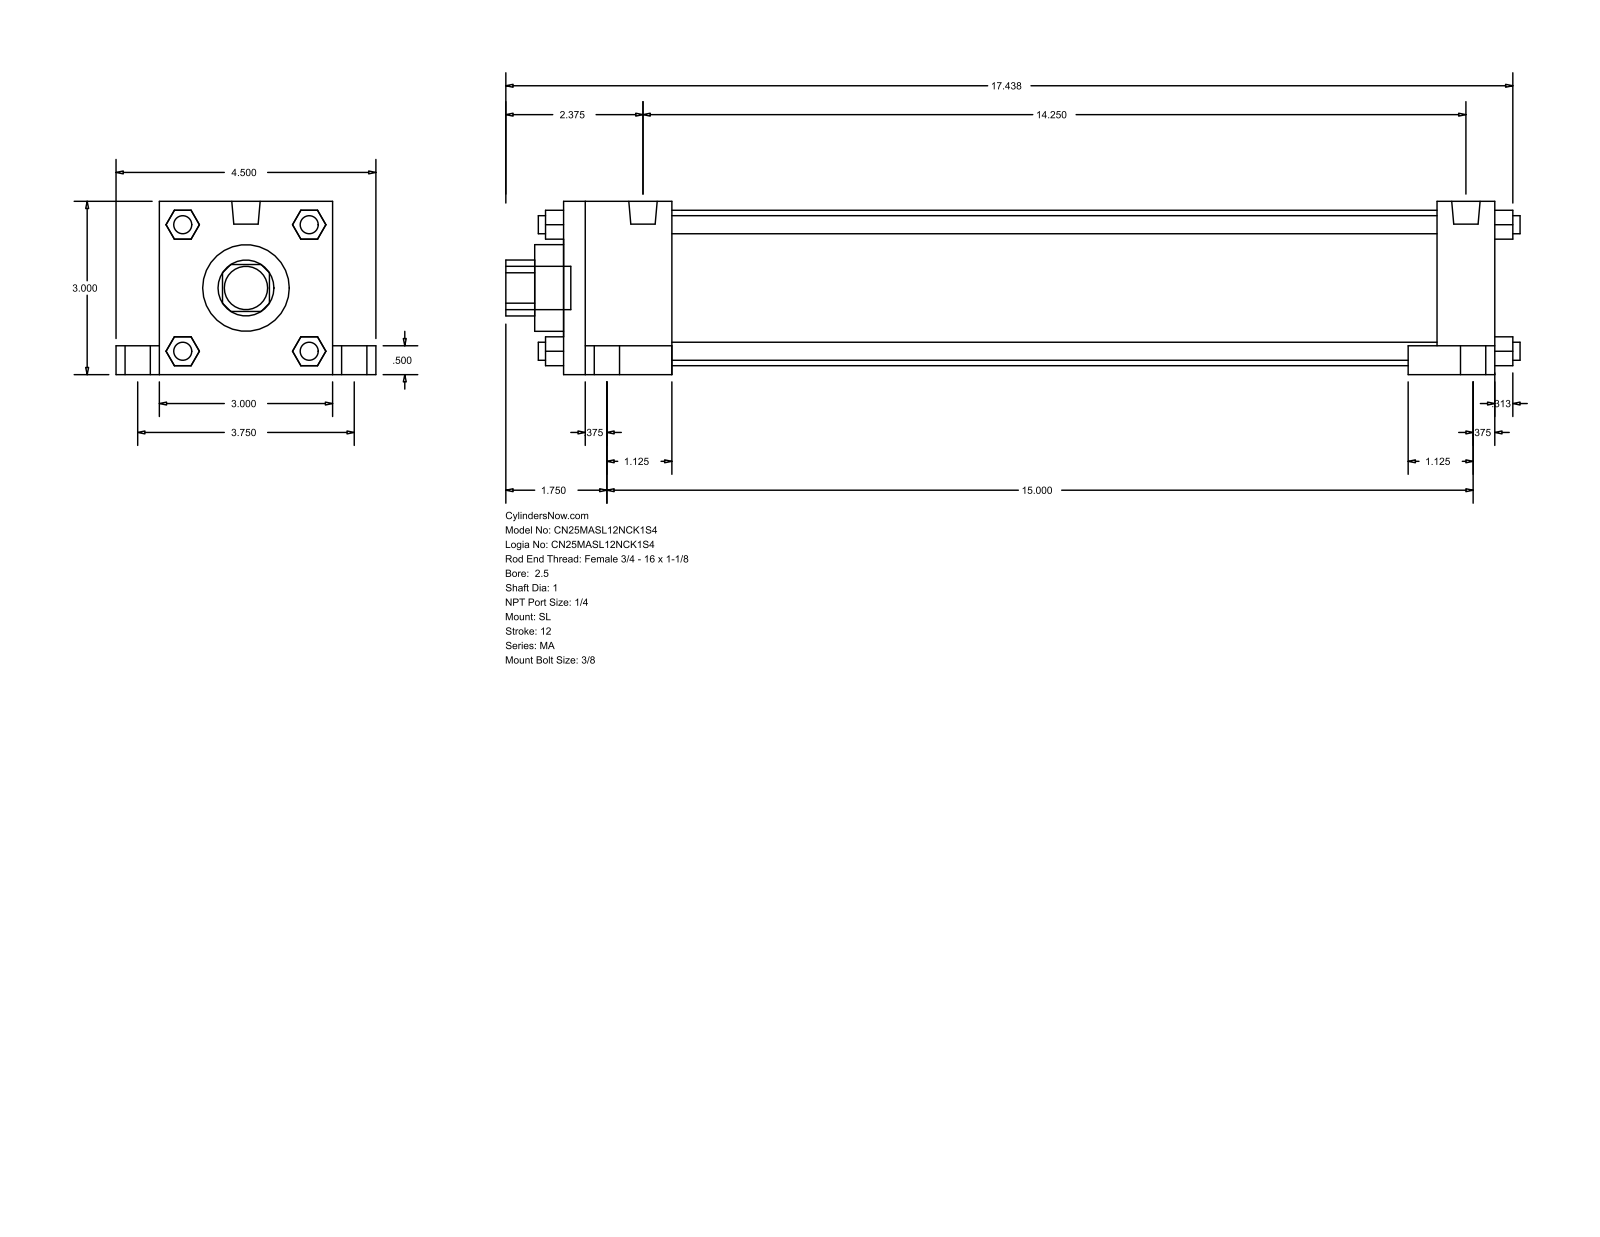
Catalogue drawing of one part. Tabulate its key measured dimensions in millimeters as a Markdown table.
| quantity | value |
| --- | --- |
| part name | MA_SL__0250_1 |
| STEP written by | GSSL Pune (CONFIG_CONTROL_DESIGN) |
| units | millimeters |
| bodies | 0 solids, 148 faces (112 planar, 36 cylindrical, 0 other) |
| overall size | 446.09 × 114.3 × 76.2 |
| round holes (diameter × count) | 25.4 × 1, 38.1 × 1, 68.33 × 1 |
| round bosses / shafts (diameter × count) | 7.94 × 8, 17.46 × 4, 11.11 × 4, 12.49 × 2, 19.05 × 1 |
| partial cylindrical surfaces (radius × count) | 12.29 × 1 |
| main face-to-face distances | 76.2, 409.58, 12.7, 47.63, 361.95, 384.17, 336.54, 25.41, 19.05, 95.25 |
